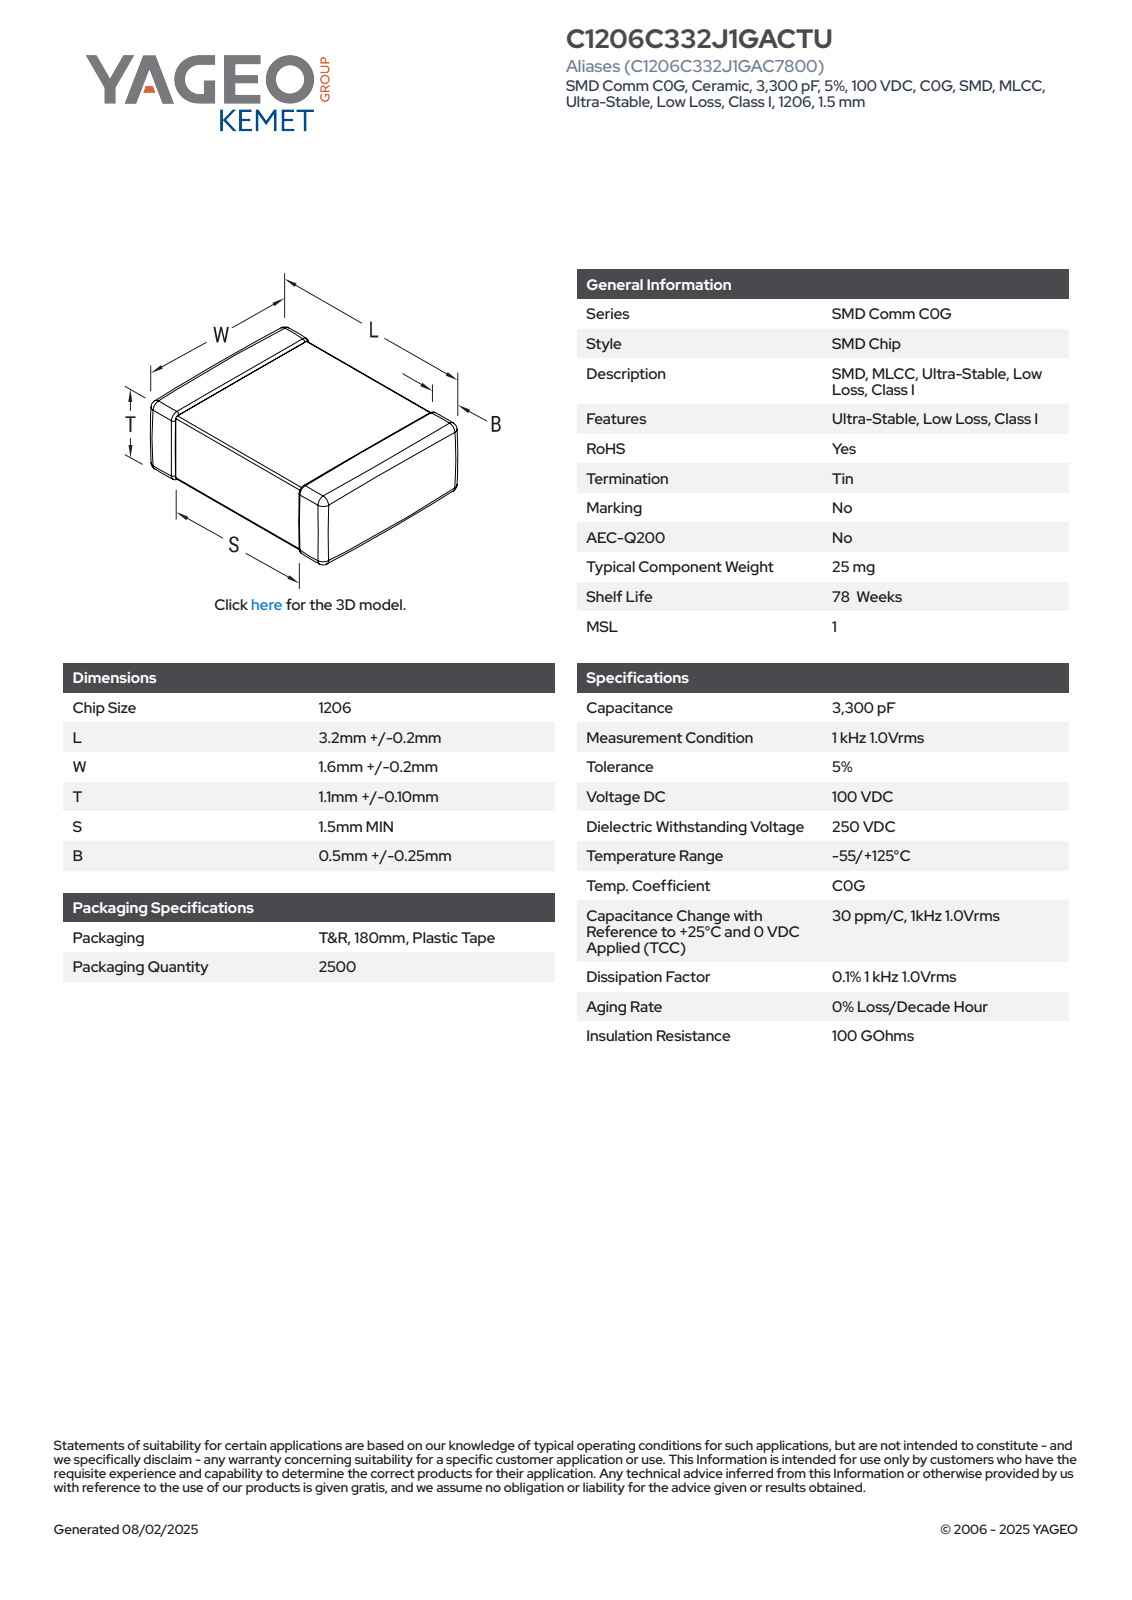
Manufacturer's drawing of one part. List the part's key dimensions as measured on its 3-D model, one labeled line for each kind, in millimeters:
Part name (STEP PRODUCT): CCS_CCSTD_1206_L3.4W1.8T1.2B0.5
STEP written by: SolidWorks 2021 (AUTOMOTIVE_DESIGN)
Units: millimetres
Bodies: 4 solids, 125 faces (71 planar, 38 cylindrical, 16 other)
Overall size (bounding box): 3.4 × 1.8 × 1.2
Volume: 7 mm³ · Surface area: 24 mm²
Main face-to-face distances: 1.16, 1.12, 1.76, 1.2, 1.72, 3.4, 1.8, 1.17, 1.13, 1.57
